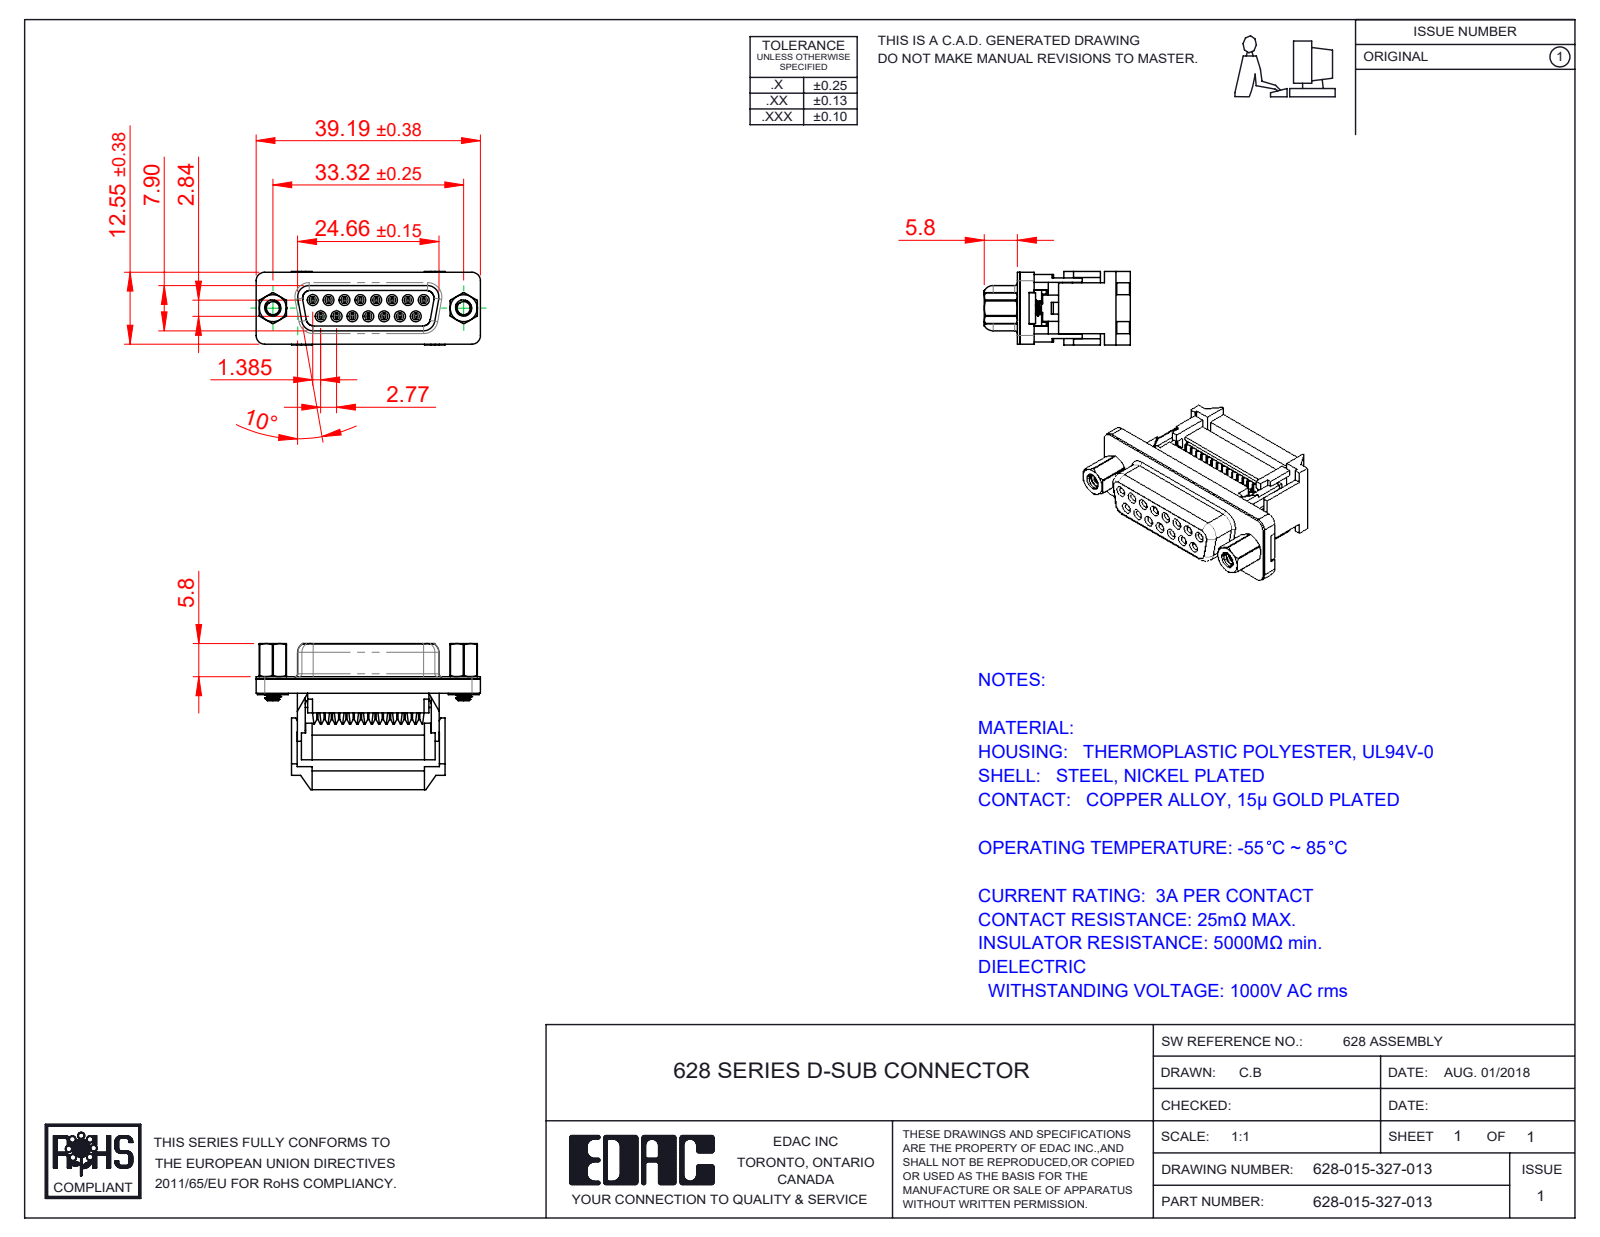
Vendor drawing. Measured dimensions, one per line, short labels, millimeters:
name: 628-015-327-013; 628 IDC Housing_15 Contacts; 628 IDC Guide Front_15 Contacts; 628 IDC Contacts_15 Contacts (+5 more)
written by: SolidWorks 2020 (CONFIG_CONTROL_DESIGN)
unit: mm
bodies: 26 solids, 2755 faces (1610 planar, 629 cylindrical, 516 other)
size: 39.19 × 25.5 × 12.85
volume: 4 542 mm³; area: 9 452 mm²
holes: 15× ⌀1.2, 2× ⌀2.26, 2× ⌀2.29, 2× ⌀4, 2× ⌀4.8, 2× ⌀5
bosses: 2× ⌀4.9, 2× ⌀2.79
rounds: 64× R0.9, 60× R1.2, 34× R0.5, 30× R0.15, 15× R0.64, 15× R0.65, 15× R0.89, 15× R0.94
face distances: 1.9, 0.4, 1.03, 5.2, 1, 7.05, 7.07, 2.33, 0.42, 8.1
hole spacings: 3.16, 2.77, 5.54, 8.31, 5.03, 7.48, 11.08, 5.04
